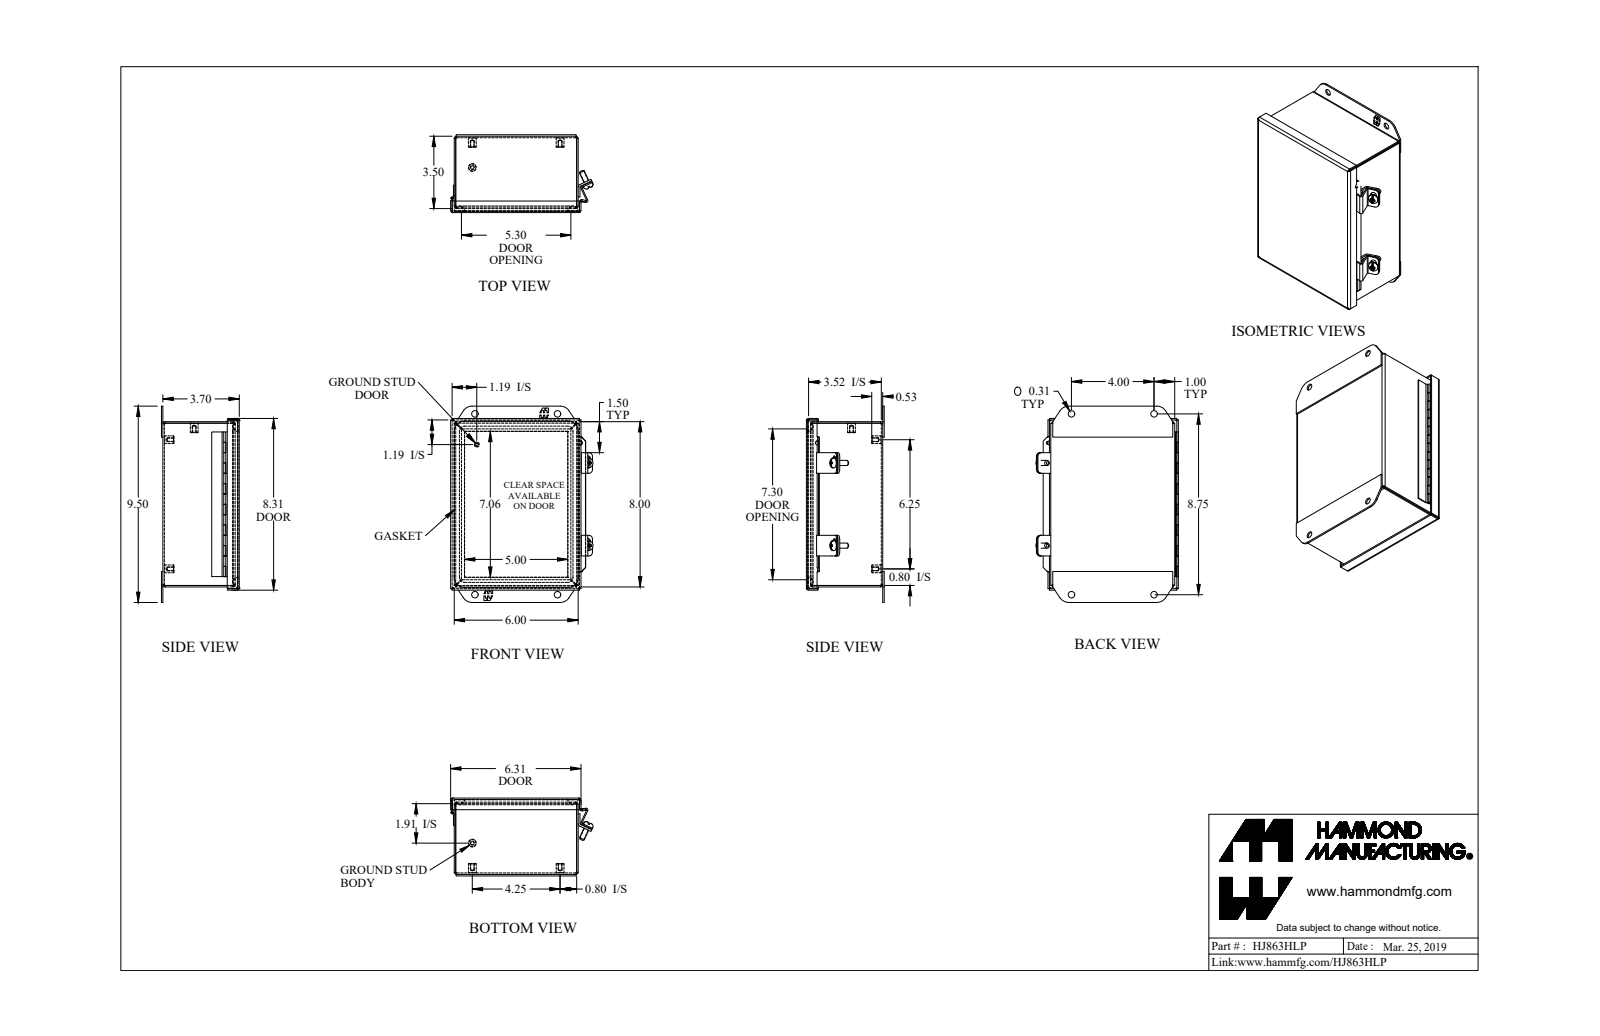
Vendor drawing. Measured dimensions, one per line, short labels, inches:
name: HJ863HLP
written by: SolidWorks 2018 (AUTOMOTIVE_DESIGN)
unit: in
bodies: 20 solids, 713 faces (382 planar, 203 cylindrical, 128 other)
size: 9.5 × 6.896 × 3.769
volume: 20.22 in³; area: 571.2 in²
holes: 5× ⌀0.156, 4× ⌀0.313, 2× ⌀0.213, 1× ⌀0.05
bosses: 5× ⌀0.375, 3× ⌀0.25, 2× ⌀0.48, 1× ⌀0.188, 1× ⌀0.1, 1× ⌀0.045
rounds: 16× R0.25, 13× R0.036, 13× R0.108, 4× R0.01, 4× R0.141, 4× R0.188, 4× R0.499, 4× R0.5
face distances: 0.072, 3.625, 3.697, 5.928, 3.553, 7.928, 6, 5.856, 8, 7.856
hole spacings: 1.256, 4.31, 7.501, 8.559, 4, 4.25, 6.25, 7.558
